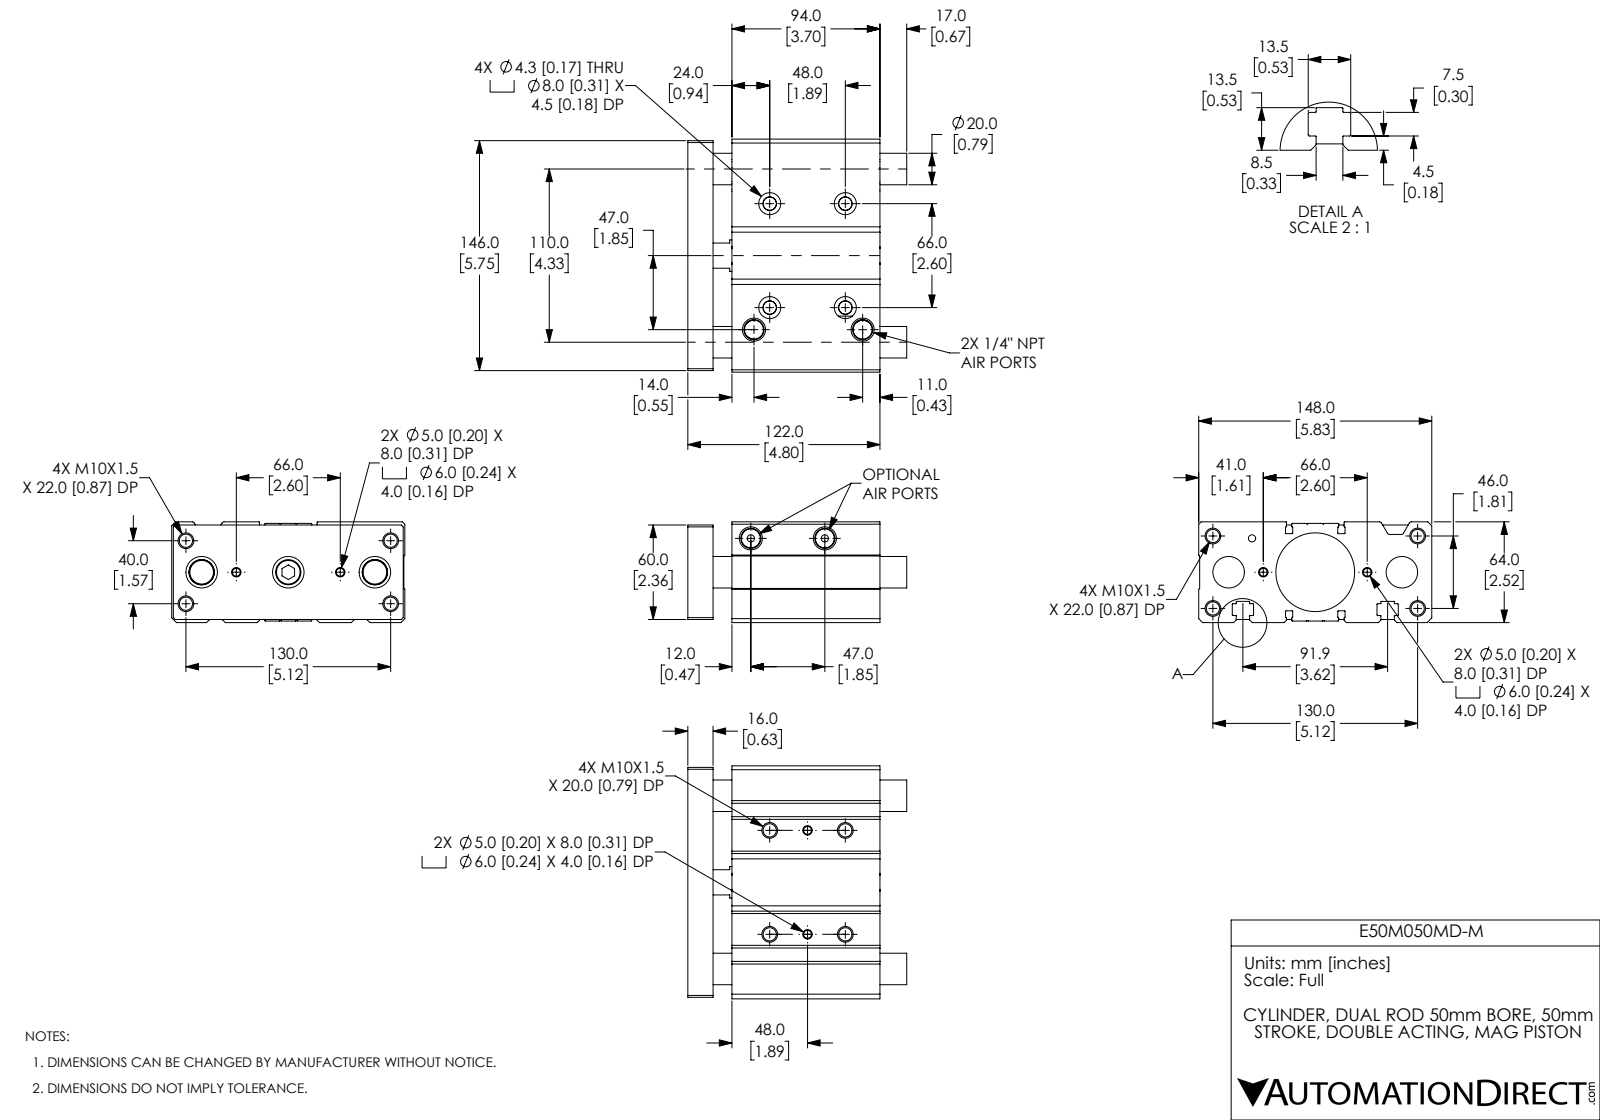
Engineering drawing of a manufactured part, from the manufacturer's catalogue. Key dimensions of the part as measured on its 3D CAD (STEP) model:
Part name (STEP PRODUCT): E50M050MD-M; E50M050MD-M_ENDPLATE; E50M050MD-M_BODY
STEP written by: SolidWorks 2019 (CONFIG_CONTROL_DESIGN)
Units: millimetres
Bodies: 5 solids, 423 faces (139 planar, 190 cylindrical, 94 other)
Overall size (bounding box): 148 × 139 × 64
Volume: 869 618 mm³ · Surface area: 170 682 mm²
Round holes (diameter × count): ⌀8.38 ×12, ⌀5 ×4, ⌀6 ×4, ⌀8.6 ×4, ⌀14 ×4, ⌀4.57 ×3, ⌀10 ×3, ⌀20 ×3, ⌀16 ×2, ⌀20 ×1, ⌀50 ×1, ⌀50 ×1
Round bosses / shafts (diameter × count): ⌀16 ×1
Partial cylindrical surfaces — rounded edges, fillets, slot ends (radius × count): R0.2 ×32, R0.4 ×28, R1.5 ×4, R0.3 ×2
Main face-to-face distances: 1, 12, 28, 16, 62, 64, 122, 106, 94, 5.5
Hole centre spacings: 3, 22.36, 24, 25.08, 37.74, 39.41, 43, 66
